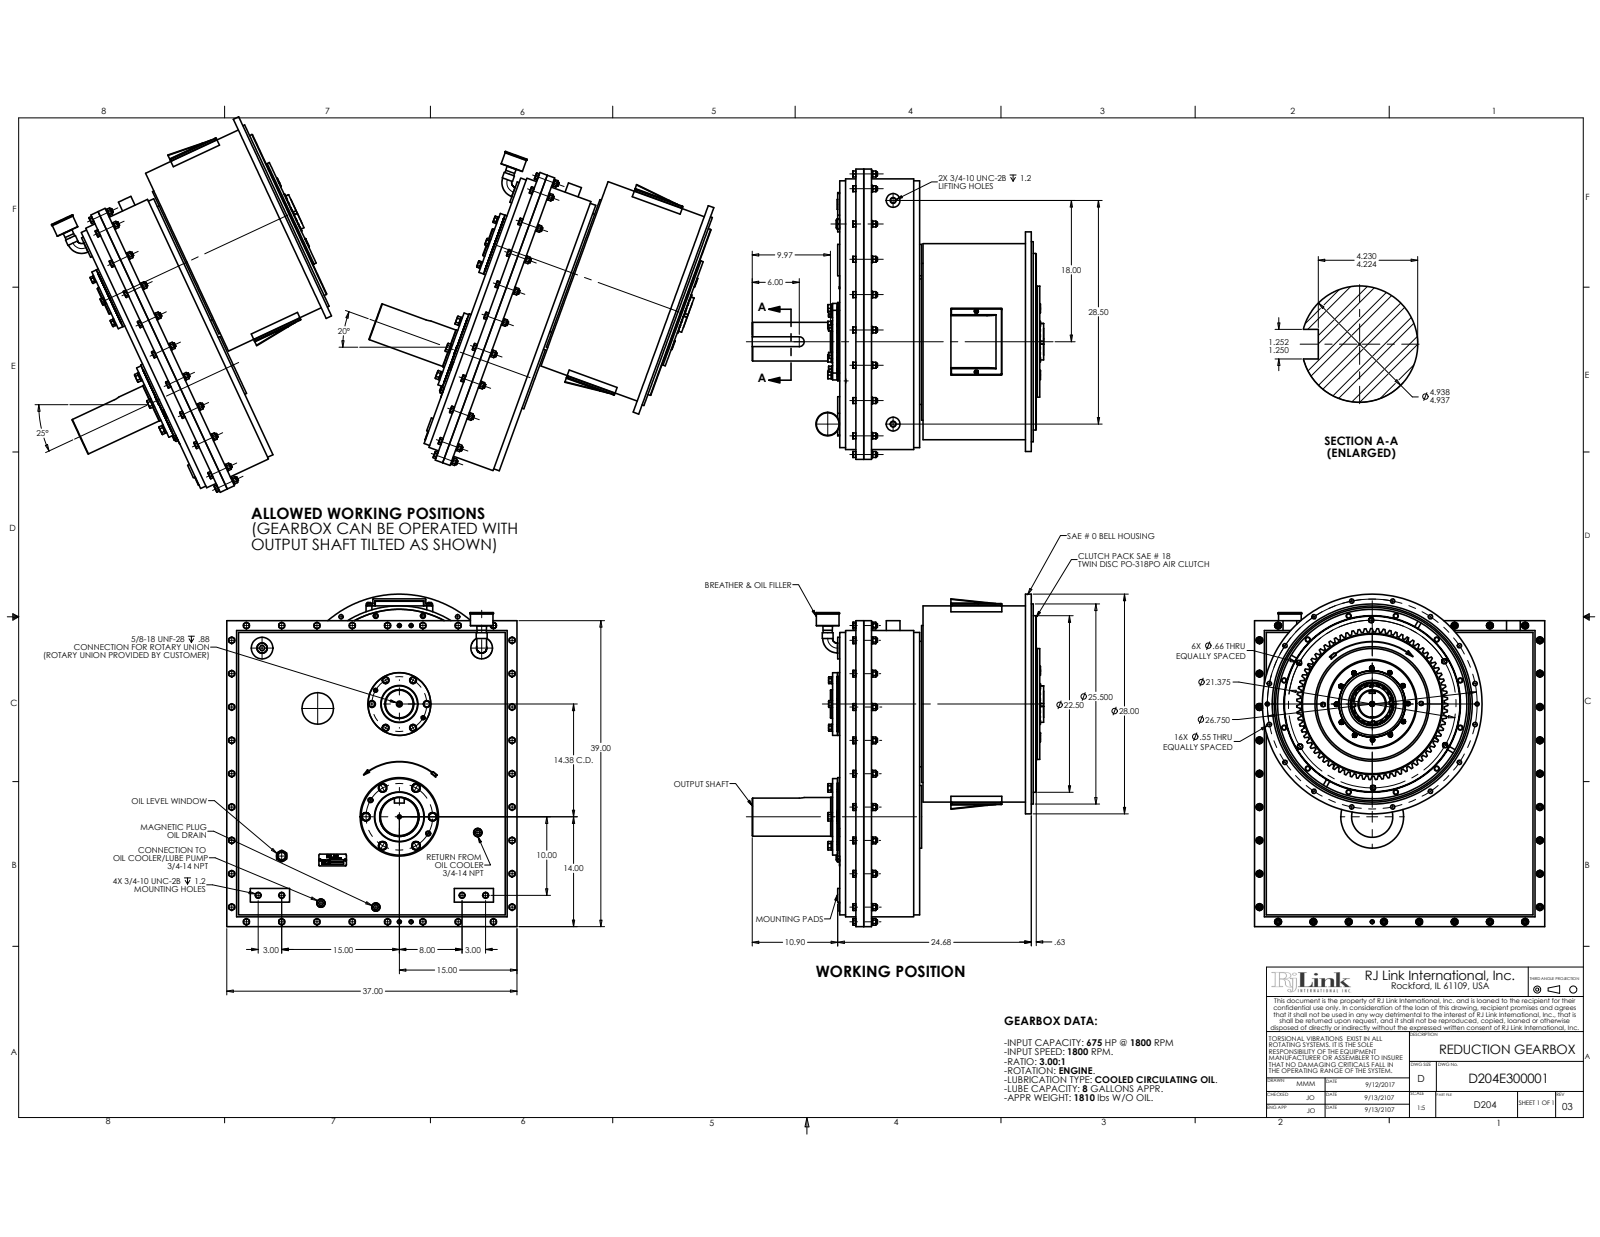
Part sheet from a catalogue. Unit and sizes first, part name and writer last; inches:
Units: inches
Overall size (bounding box): 42.375 × 37.161 × 37
Round holes (diameter × count): ⌀0.531 ×68, ⌀0.509 ×46, ⌀0.5 ×36, ⌀0.422 ×18, ⌀0.656 ×18, ⌀0.547 ×16, ⌀0.203 ×13, ⌀0.636 ×12, ⌀0.281 ×9, ⌀0.562 ×7, ⌀0.66 ×6, ⌀0.312 ×5
Round bosses / shafts (diameter × count): ⌀0.873 ×46, ⌀0.749 ×46, ⌀0.438 ×46, ⌀0.748 ×34, ⌀0.5 ×30, ⌀0.625 ×27, ⌀0.563 ×24, ⌀0.25 ×15
Partial cylindrical surfaces — rounded edges, fillets, slot ends (radius × count): R0.014 ×38, R0.06 ×30, R0.25 ×16, R0.125 ×10, R0.31 ×8, R0.375 ×6, R0.5 ×6, R0.62 ×6
Main face-to-face distances: 0.75, 9.437, 0.25, 0.5, 1, 10.187, 8.687, 6.375, 7.375, 34
Hole centre spacings: 4.25, 4.5, 7.361, 9, 10.071, 3, 13.5, 4.25
Volume: 506.3 in³ · Surface area: 16 707 in²
Bodies: 147 solids, 6261 faces (2684 planar, 2590 cylindrical, 987 other)
Part name (STEP PRODUCT): HNZ_50-13; LWZ_50; D204002; D17-0-A-18_3 (+8 more)
STEP written by: SolidWorks 2017 (AUTOMOTIVE_DESIGN)
